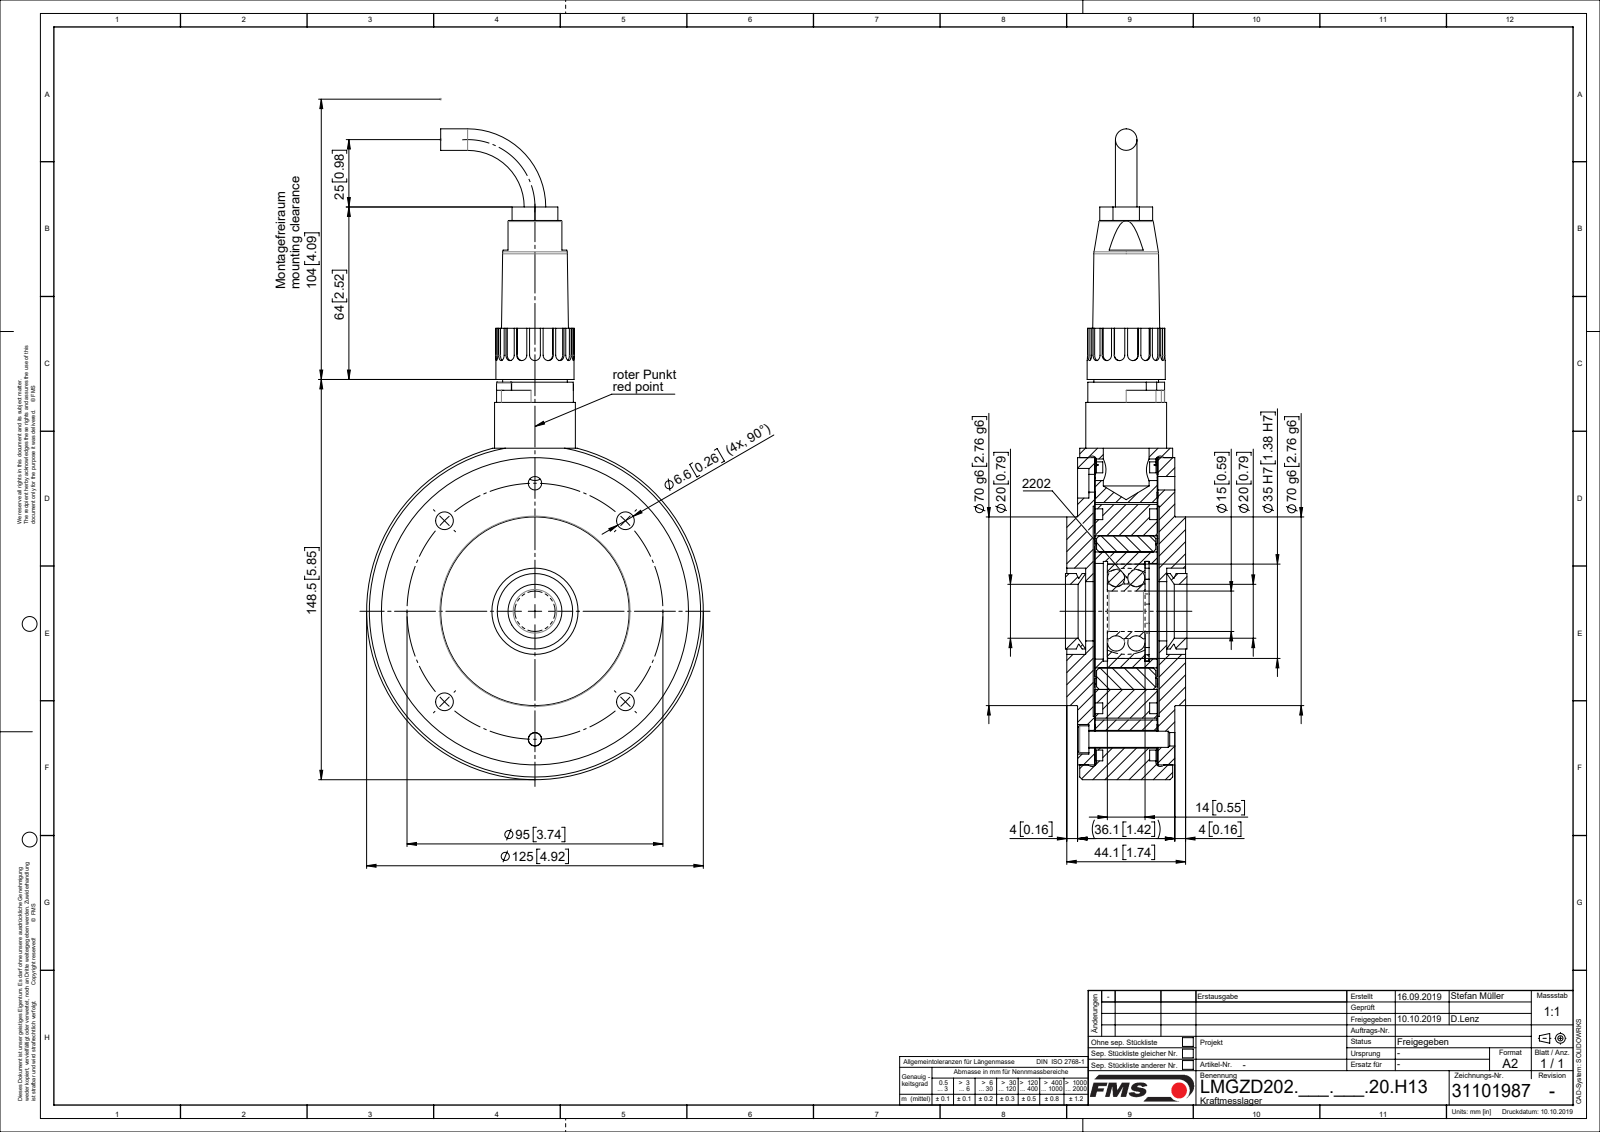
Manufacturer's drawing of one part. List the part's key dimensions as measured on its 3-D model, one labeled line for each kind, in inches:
Part name (STEP PRODUCT): Flanschstecker_Kunstst_7Pol_01; 51064_01; 49366_01; PKL_2202_01 (+8 more)
STEP written by: SolidWorks 2018 (CONFIG_CONTROL_DESIGN)
Units: inches
Bodies: 39 solids, 669 faces (166 planar, 375 cylindrical, 128 other)
Overall size (bounding box): 9.508 × 4.921 × 1.776
Volume: 28.62 in³ · Surface area: 234.4 in²
Round holes (diameter × count): ⌀0.098 ×6, ⌀0.26 ×6, ⌀0.268 ×4, ⌀0.134 ×2, ⌀0.142 ×2, ⌀0.197 ×2, ⌀0.315 ×2, ⌀0.433 ×2, ⌀0.866 ×2, ⌀0.236 ×1, ⌀0.413 ×1, ⌀0.551 ×1
Round bosses / shafts (diameter × count): ⌀0.085 ×7, ⌀0.217 ×2, ⌀0.118 ×2, ⌀4.921 ×1, ⌀4.488 ×1, ⌀4.055 ×1, ⌀2.756 ×1, ⌀2.677 ×1
Partial cylindrical surfaces — rounded edges, fillets, slot ends (radius × count): R0.079 ×17, R0.197 ×8, R0.004 ×4, R0.354 ×4, R0.118 ×2, R0.141 ×2, R0.516 ×1, R0.633 ×1
Main face-to-face distances: 0.915, 0.248, 0.258, 1.163, 1.173, 0.906, 0.935, 0.925, 0.03, 0.228
Hole centre spacings: 1.87, 0.64, 0.906, 1.365, 1.431, 2.645, 2.659, 3.456
